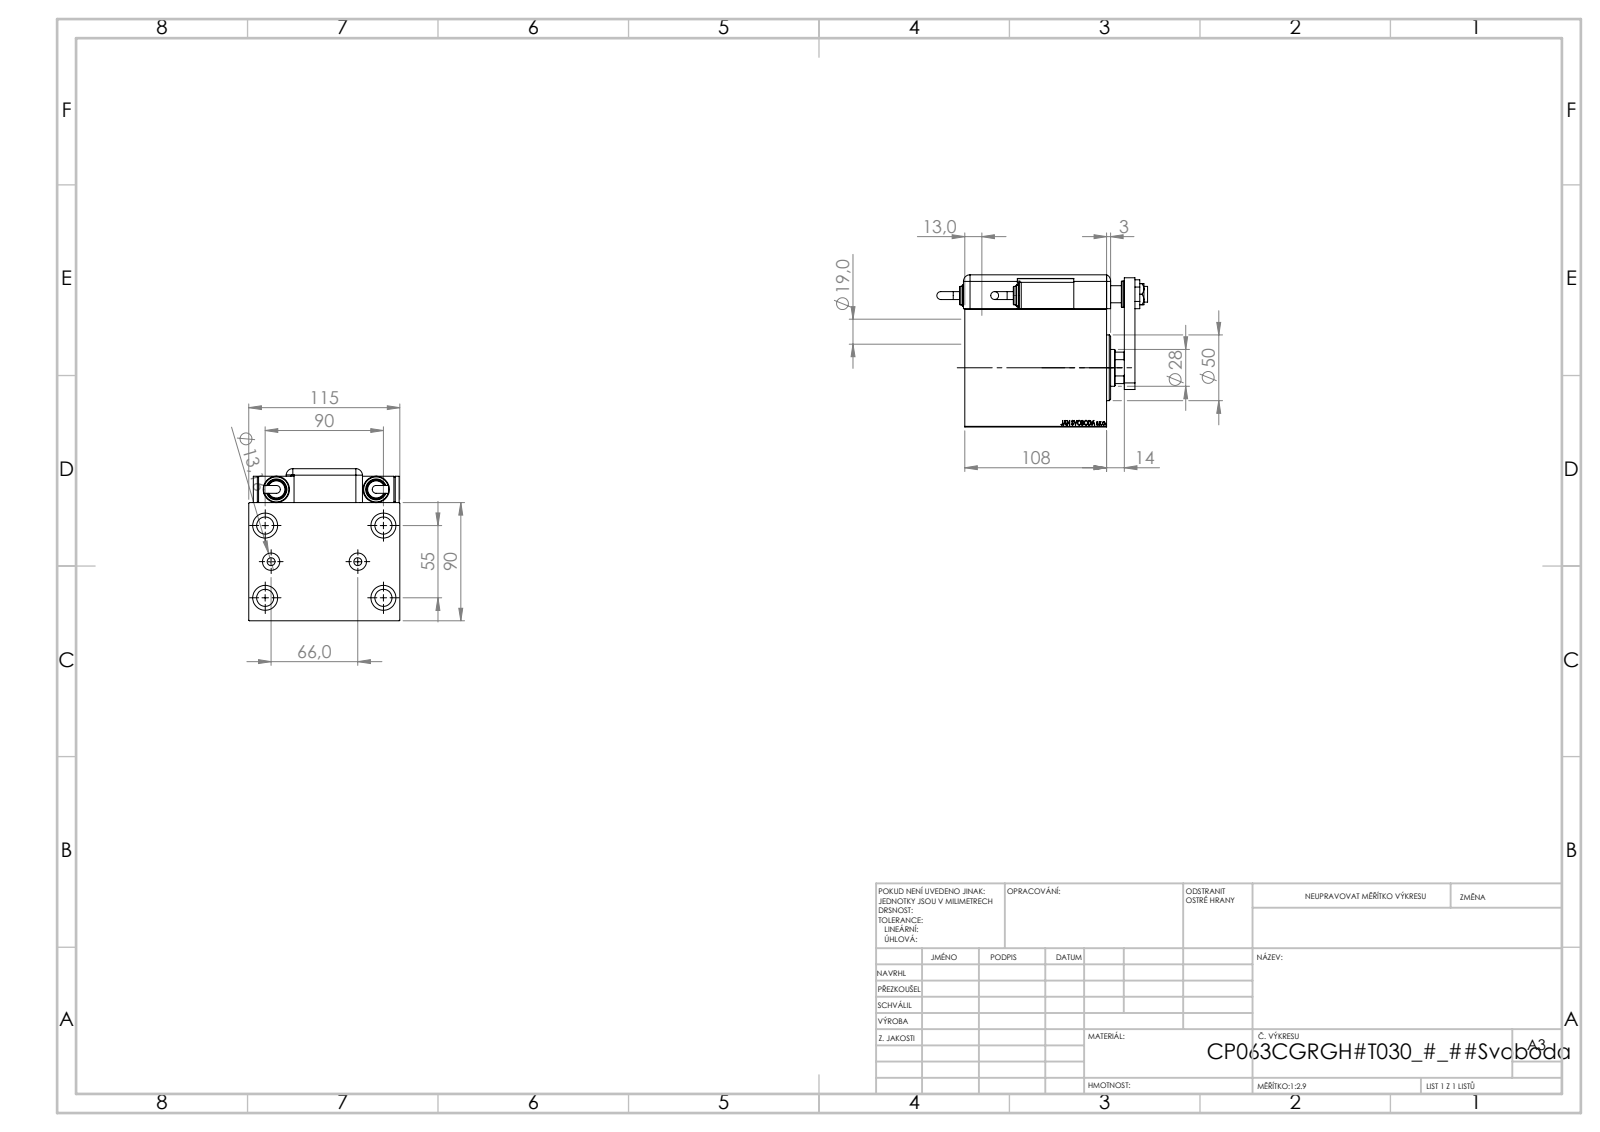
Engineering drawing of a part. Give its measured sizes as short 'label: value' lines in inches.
name: SWITCH_Q_FRONT_BACK; MAGNETIC SWITCH Q; TYC; NUT_D19 (+7 more)
written by: SolidWorks 2019 (CONFIG_CONTROL_DESIGN)
unit: in
bodies: 13 solids, 1244 faces (614 planar, 113 cylindrical, 517 other)
size: 6.317 × 4.559 × 4.528
volume: 68.1 in³; area: 302.5 in²
holes: 5× ⌀0.512, 4× ⌀0.748, 2× ⌀0.157, 2× ⌀0.236, 2× ⌀0.315, 2× ⌀0.518, 1× ⌀0.472, 1× ⌀0.551, 1× ⌀0.728, 1× ⌀0.787, 1× ⌀1.102, 1× ⌀1.24
bosses: 3× ⌀0.787, 2× ⌀0.63, 2× ⌀0.551, 2× ⌀0.236, 1× ⌀1.969
rounds: 9× R0.197, 1× R0.394, 1× R0.531
face distances: 3.543, 0.118, 4.528, 4.252, 3.563, 0.689, 0.531, 0.315, 1.016, 4.559
hole spacings: 2.076, 2.097, 1.097, 1.327, 2.056, 2.165, 2.979, 3.536
